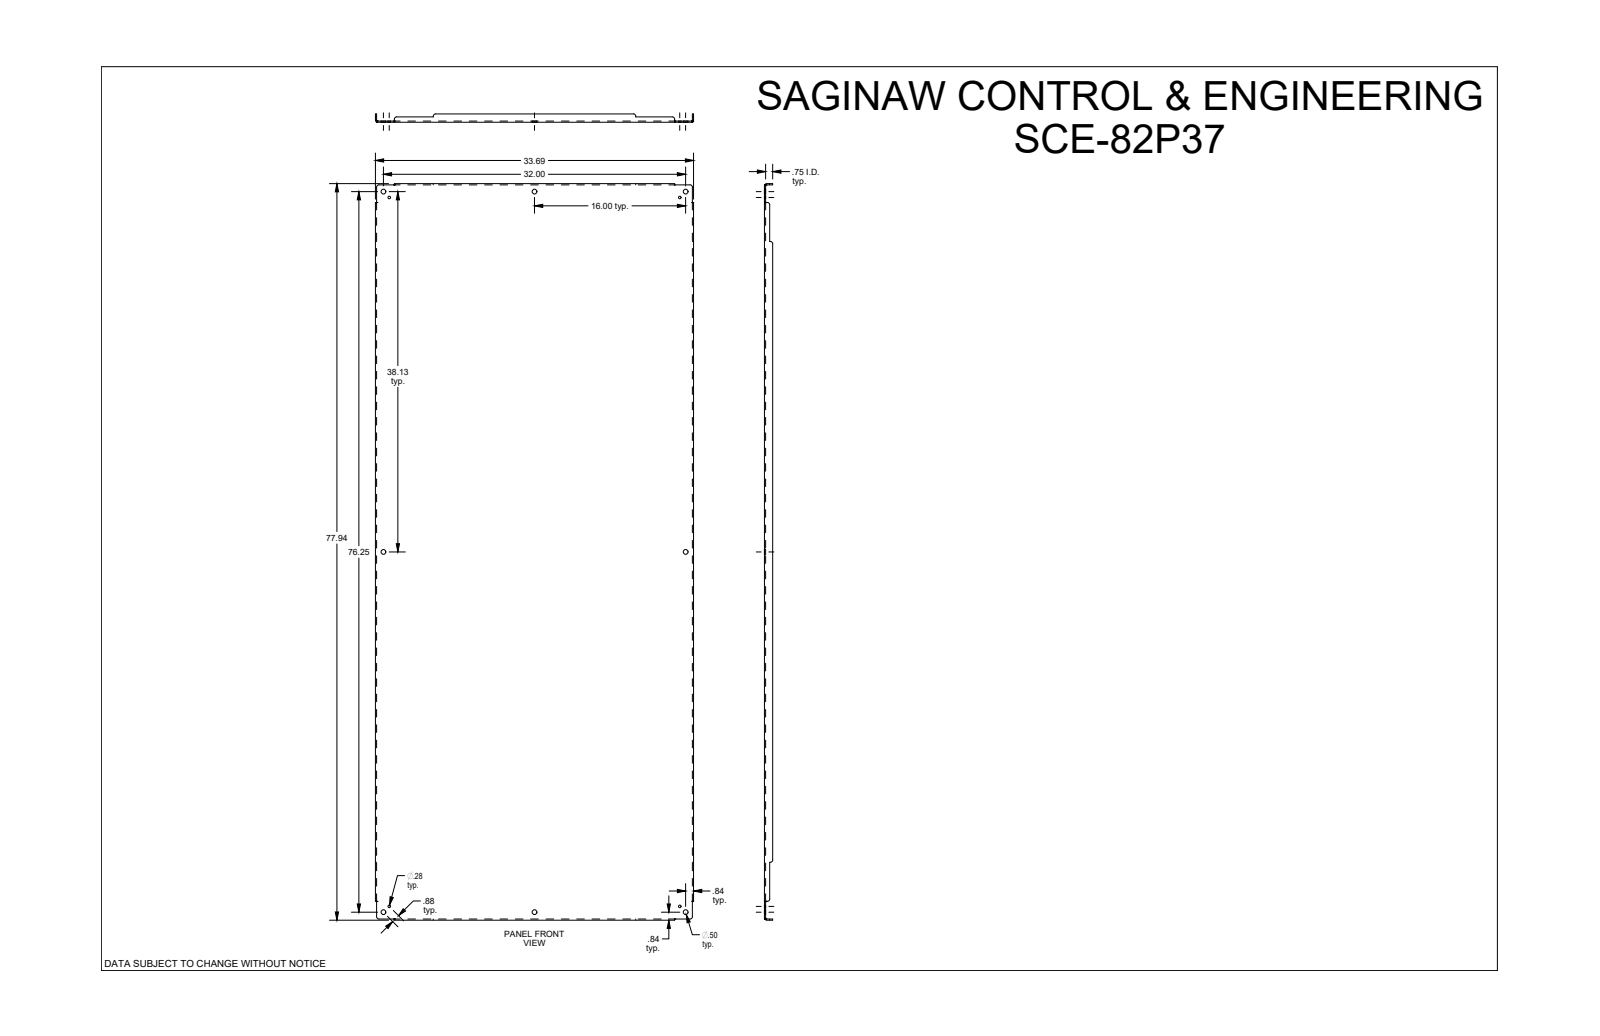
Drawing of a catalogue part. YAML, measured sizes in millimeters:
part_name: "SCE-82P37"
step_written_by: "SolidWorks 2019 (CONFIG_CONTROL_DESIGN)"
units: millimeters
bodies: {solids: 1, faces: 110, planar: 46, cylindrical: 40, other: 24}
overall_size: [1979.6, 855.7, 22.2]
volume: 5636000
surface_area: 3570000
round_holes:
  - {diameter: 12.7, count: 8}
  - {diameter: 7.1, count: 4}
partial_cylinders:
  - {radius: 6.4, count: 12}
  - {radius: 2.8, count: 4}
  - {radius: 6, count: 4}
face_to_face_distances: [3.2, 852.5, 849.3, 855.6, 3.2, 1976.5, 19.1, 22.2, 1973.2, 1979.6]
hole_center_spacings: [22.2, 391, 406.4, 797.2, 952.8, 968.4, 1050.2, 1242.1]
